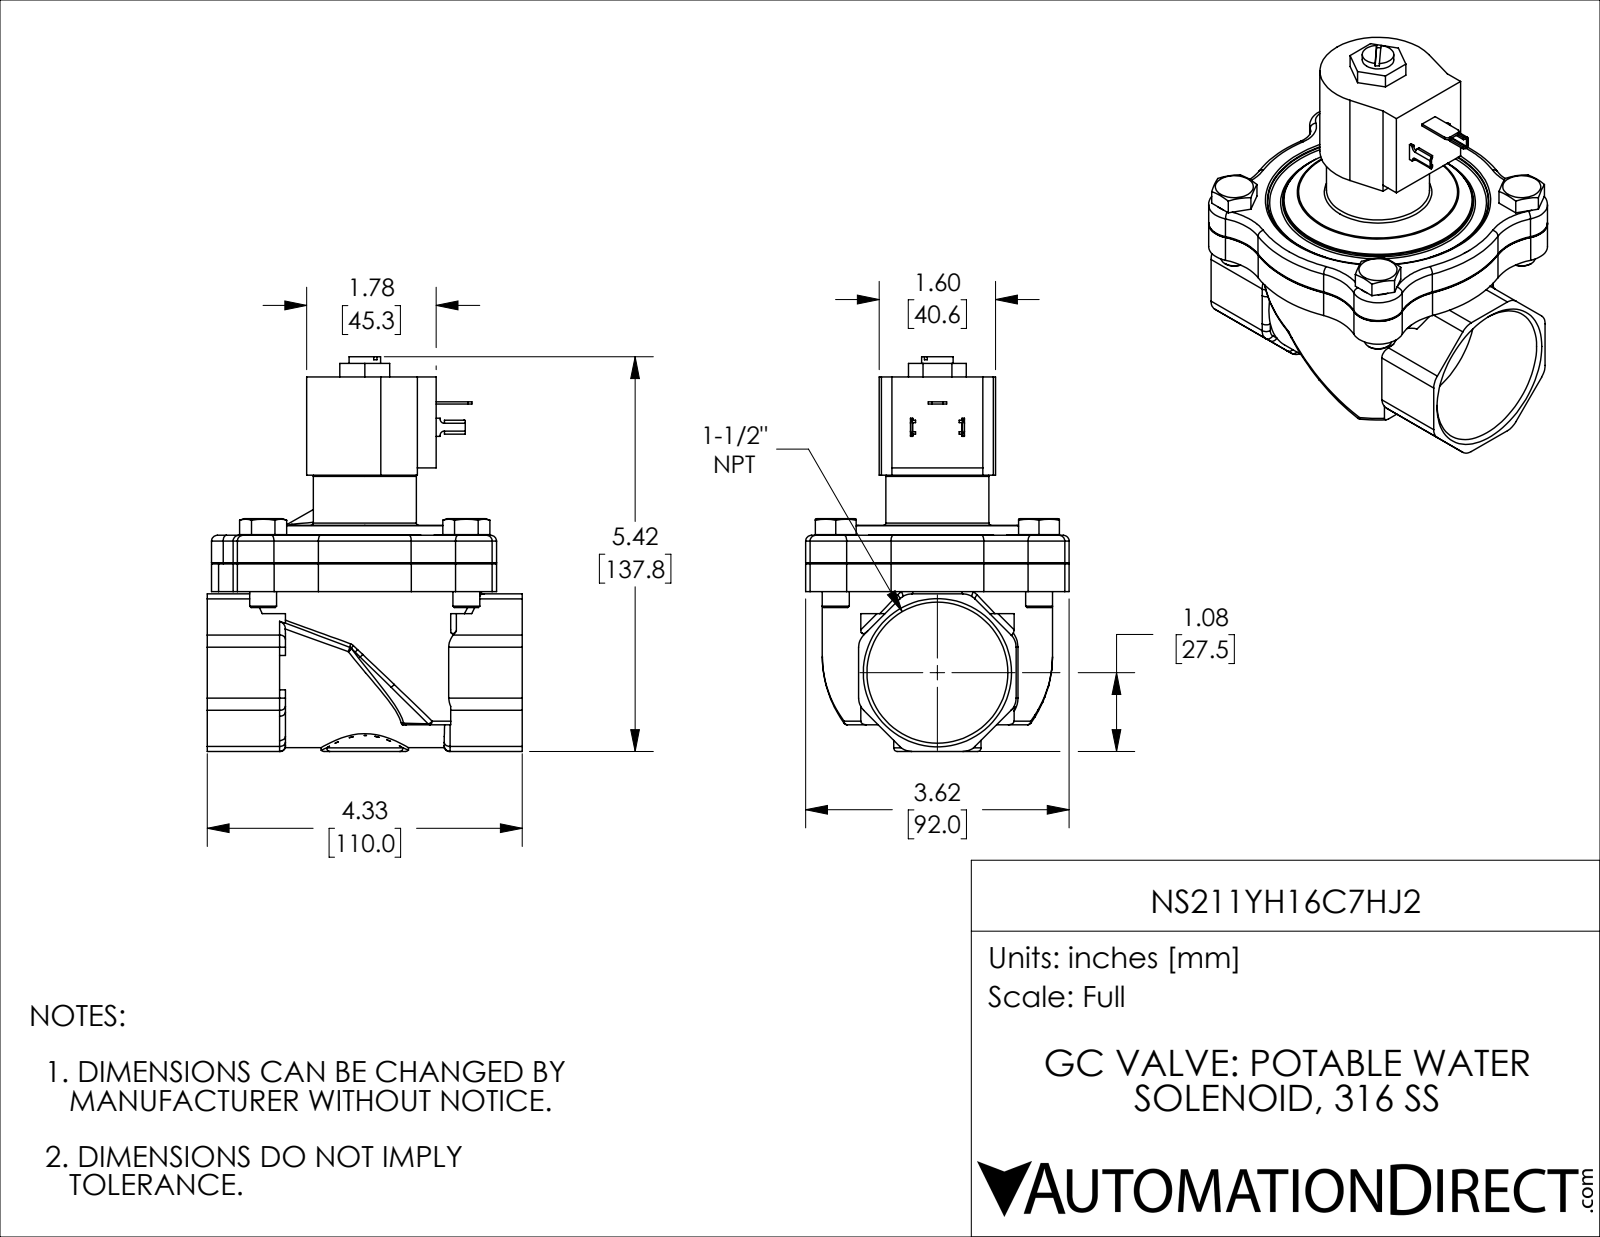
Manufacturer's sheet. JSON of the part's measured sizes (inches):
{"part_name": "NS211YH16C7HJ2", "step_written_by": "SolidWorks 2024 (CONFIG_CONTROL_DESIGN)", "units": "inches", "bodies": {"solids": 9, "faces": 520, "planar": 159, "cylindrical": 158, "other": 203}, "overall_size": [5.424, 4.33, 3.622], "volume_in3": 25.63, "surface_area_in2": 136.4, "round_holes": [[0.375, 4], [0.433, 4], [0.125, 1], [0.434, 1], [0.846, 1], [0.949, 1], [1.937, 1]], "round_bosses_or_shafts": [[0.504, 4], [0.37, 4], [3.165, 1], [1.417, 1], [1.2, 1]], "partial_cylinders_radius": [[0.787, 15], [0.08, 13], [0.236, 8], [0.354, 8], [0.006, 4], [0.041, 4], [0.05, 2], [0.06, 2]], "face_to_face_distances": [0.382, 0.775, 0.393, 1.83, 1.602, 1.22, 0.827, 2.952, 2.57, 2.177], "hole_center_spacings": [2.795, 1.976, 1.977, 2.794, 2.795, 3.952, 3.953]}
